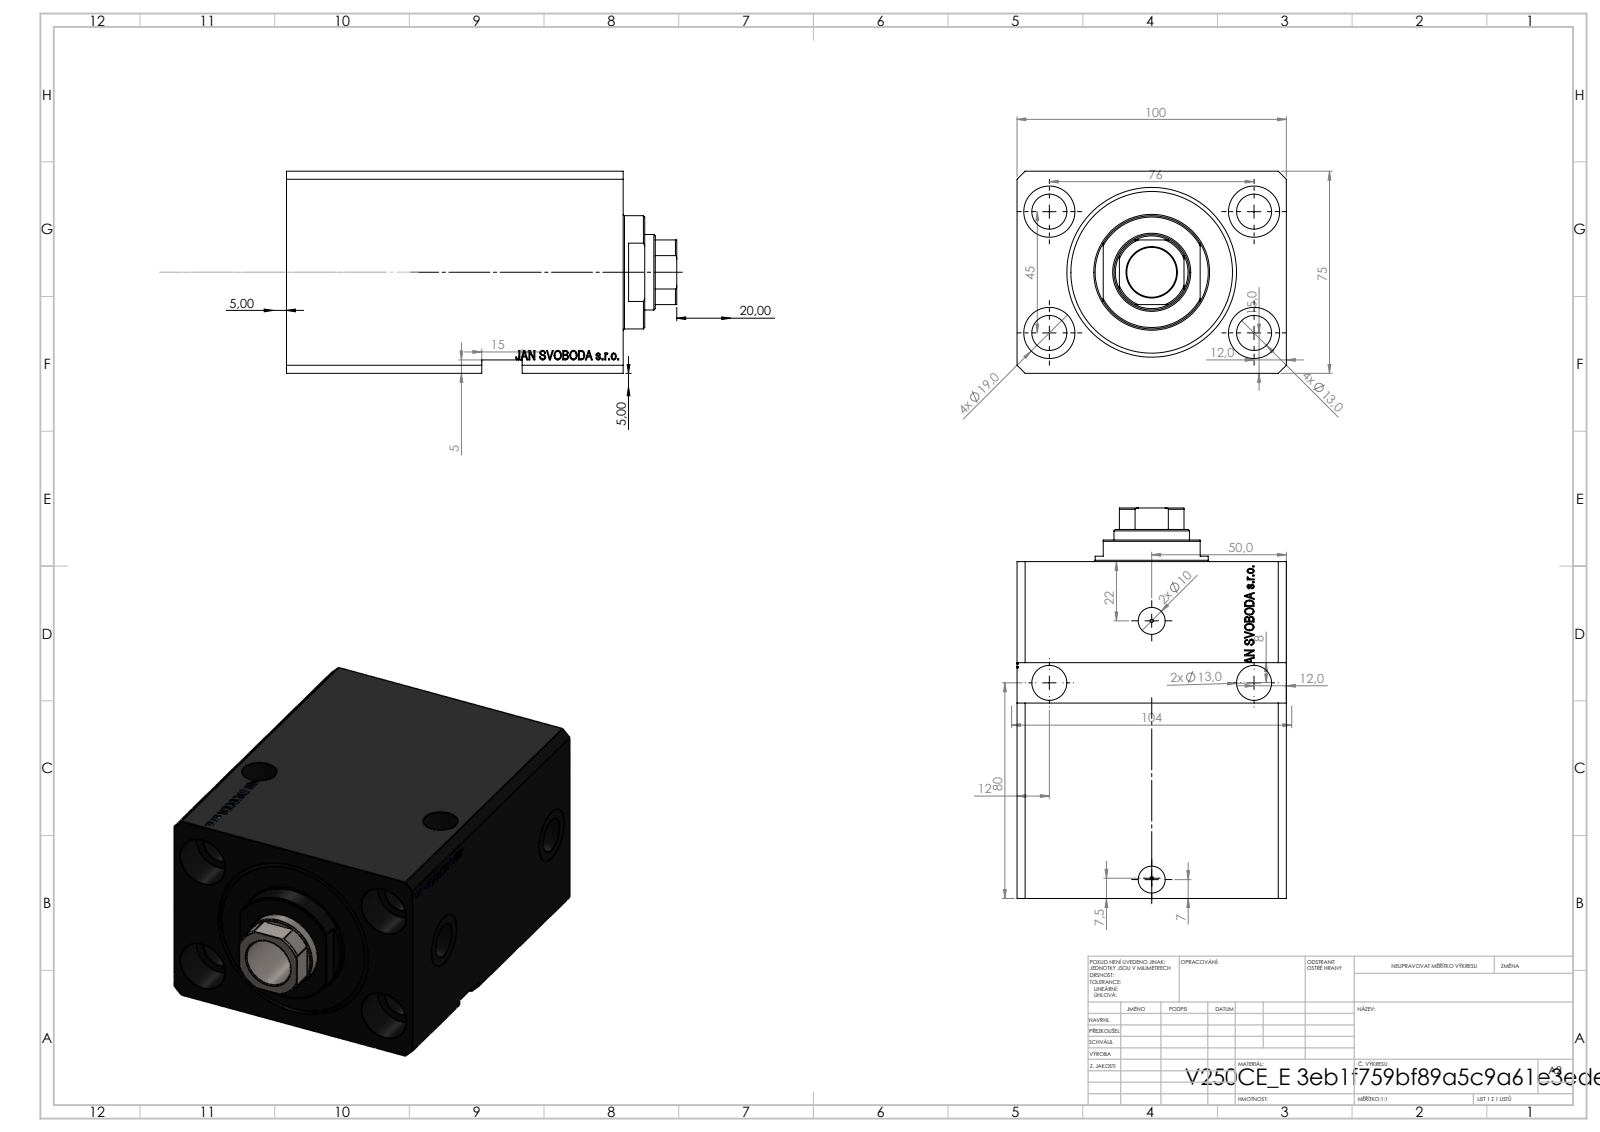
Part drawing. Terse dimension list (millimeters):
name: V250CE_VC_E; V250CE_E_Body; V250CE_C_VCP
written by: SolidWorks 2019 (CONFIG_CONTROL_DESIGN)
unit: mm
bodies: 3 solids, 938 faces (459 planar, 104 cylindrical, 375 other)
size: 145 × 100 × 75
volume: 754 695 mm³; area: 138 585 mm²
holes: 8× ⌀13, 4× ⌀1.25, 4× ⌀19, 2× ⌀10, 2× ⌀13.16, 2× ⌀20, 1× ⌀18.5, 1× ⌀28, 1× ⌀50, 1× ⌀63
bosses: 1× ⌀42
rounds: 1× R13.5
face distances: 75, 100, 125, 11.9, 113.1, 20, 105, 93.1, 70, 13
hole spacings: 44.16, 76, 40, 44.42, 45, 49.98, 50.33, 73.57
